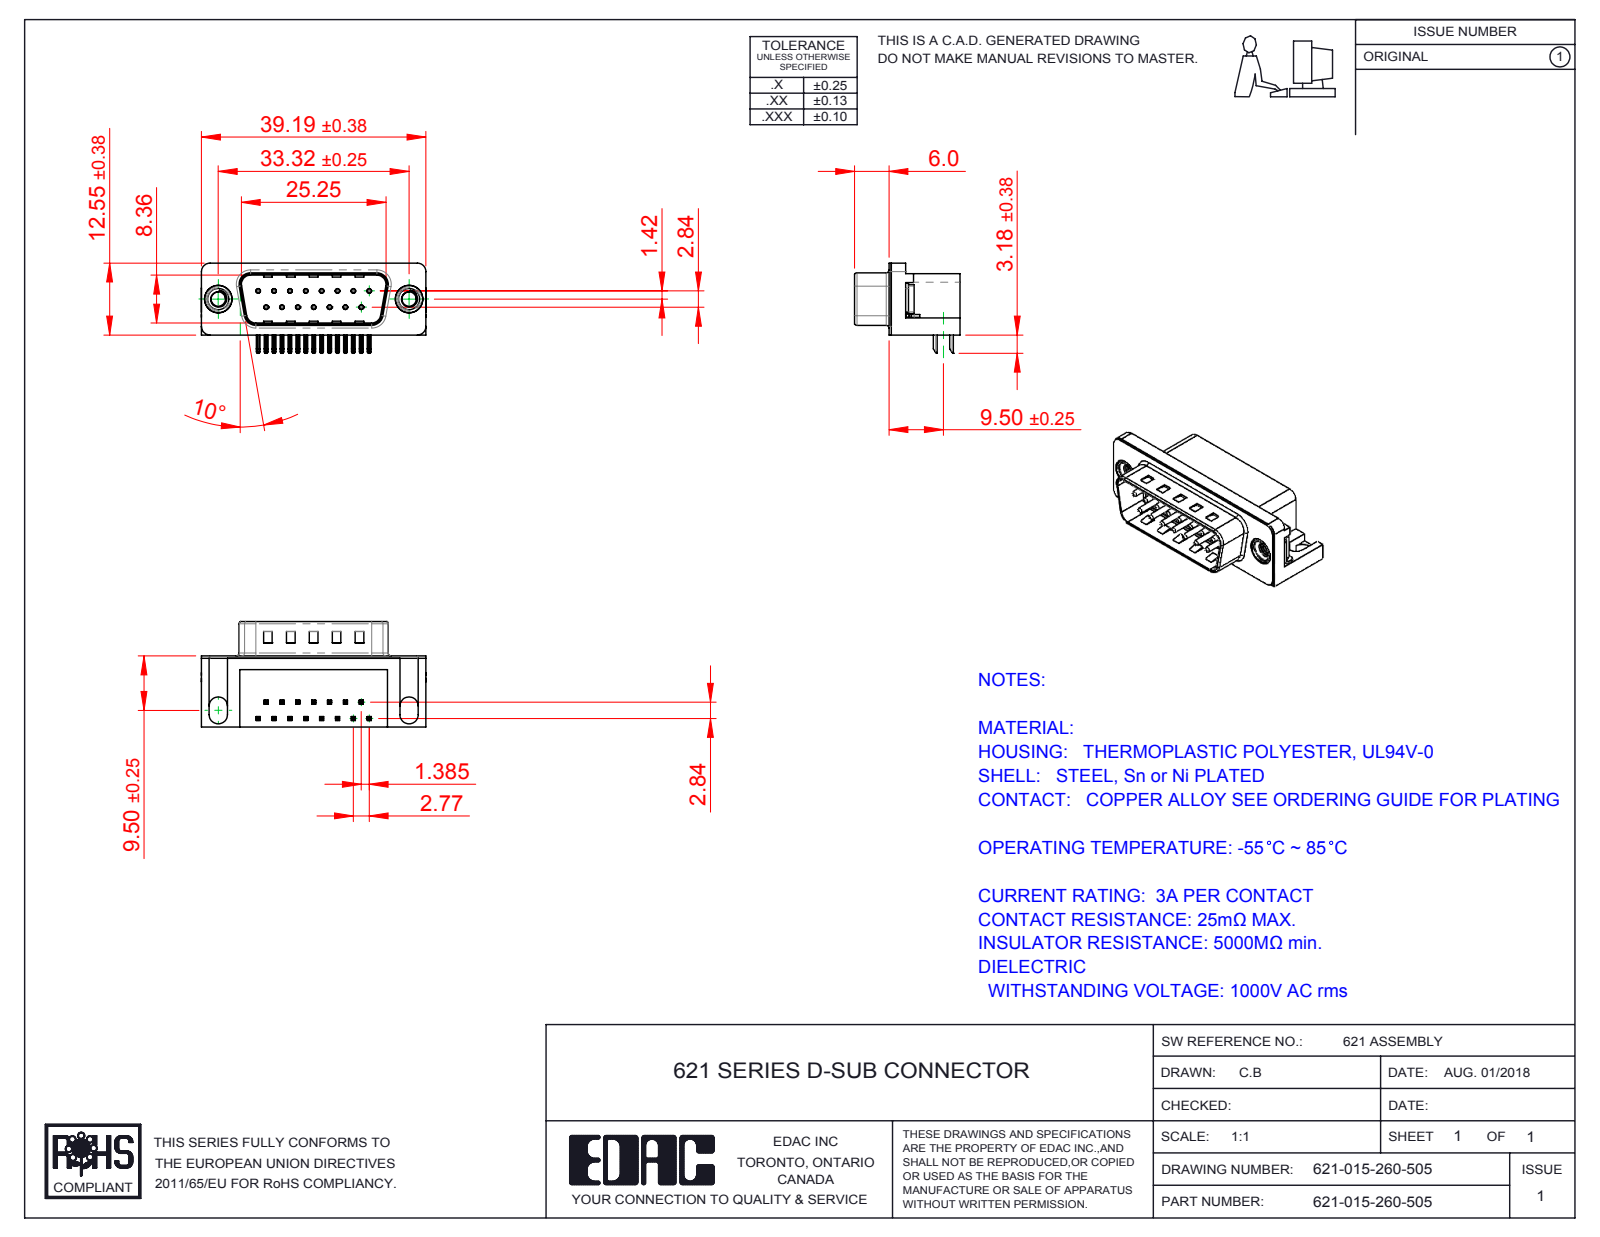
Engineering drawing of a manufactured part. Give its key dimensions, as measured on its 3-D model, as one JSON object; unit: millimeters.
{"part_name": "621 Housing_15 Socket; 621 Shell_15 Socket; 621 Contact Bottom; 621 Non Board Mount (+3 more)", "step_written_by": "SolidWorks 2016 (CONFIG_CONTROL_DESIGN)", "units": "millimeters", "bodies": {"solids": 21, "faces": 1471, "planar": 891, "cylindrical": 445, "other": 135}, "overall_size": [39.22, 18.4, 15.73], "volume_mm3": 4374, "surface_area_mm2": 5481, "round_holes": [[0.35, 15], [0.8, 15], [2.5, 2], [4, 2], [4.8, 2], [5, 2]], "round_bosses_or_shafts": [[0.75, 15], [4.9, 2], [4.75, 2], [3.9, 2]], "partial_cylinders_radius": [[0.25, 68], [0.12, 30], [1, 16], [0.5, 9], [1.6, 8], [1.5, 6], [0.9, 4], [2, 4]], "face_to_face_distances": [0.4, 12, 10.35, 2.1, 10.46, 12.4, 1.7, 10.86, 8.76, 2.9], "hole_center_spacings": [3.16, 2.77, 5.54, 8.31, 11.08, 5.03, 5.04, 7.48]}
